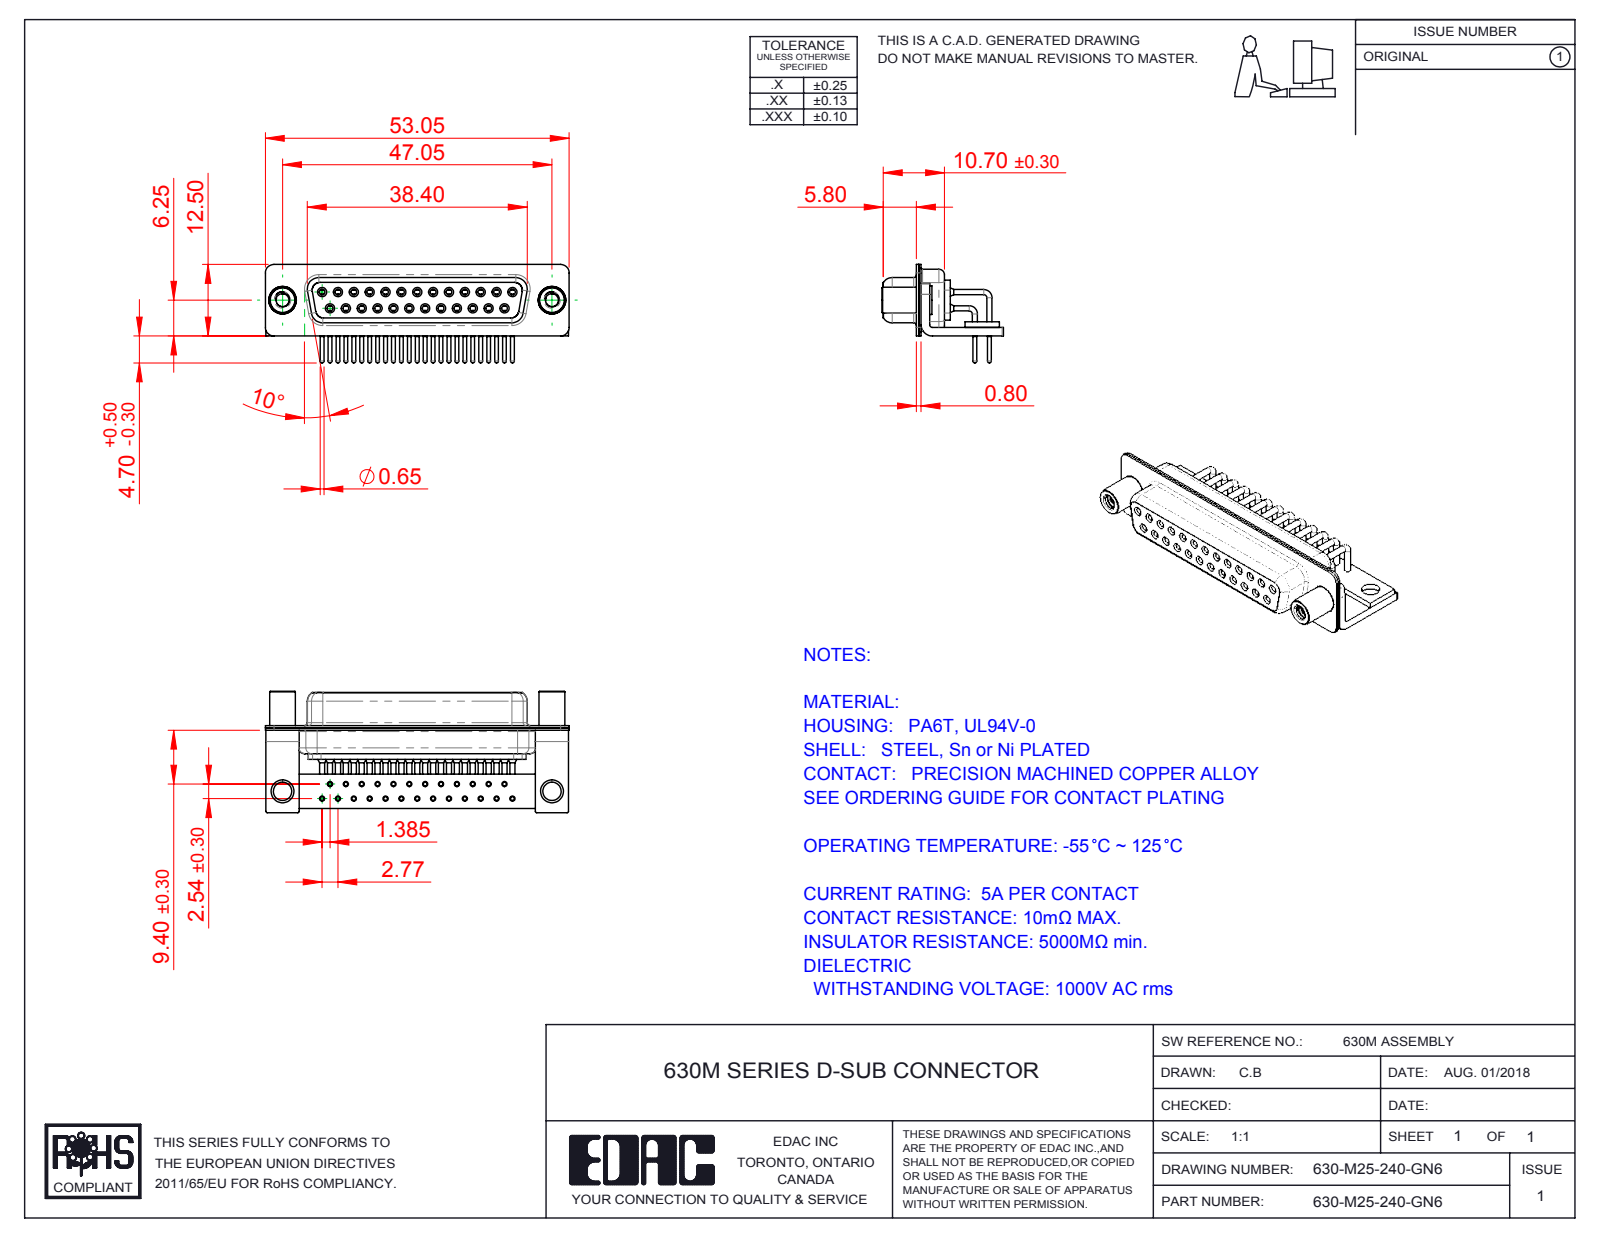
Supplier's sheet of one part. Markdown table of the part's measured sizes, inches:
| quantity | value |
| --- | --- |
| part name | 630M Contact Row 1; 630-M25-240-GN6; 630M Shell Front_25 Contacts; 630M Contact Row 2 (+5 more) |
| STEP written by | SolidWorks 2016 (CONFIG_CONTROL_DESIGN) |
| units | inches |
| bodies | 33 solids, 1754 faces (470 planar, 826 cylindrical, 458 other) |
| overall size | 2.089 × 0.835 × 0.677 |
| volume | 0.279 in³ |
| surface area | 17.7 in² |
| round holes (diameter × count) | 0.035 × 25, 0.039 × 25, 0.043 × 25, 0.067 × 25, 0.071 × 25, 0.079 × 25, 0.089 × 2, 0.126 × 2, 0.157 × 2, 0.189 × 2 |
| round bosses / shafts (diameter × count) | 0.063 × 25, 0.059 × 25, 0.035 × 25, 0.026 × 25, 0.197 × 2, 0.193 × 2, 0.177 × 2 |
| partial cylindrical surfaces (radius × count) | 0.01 × 16, 0.059 × 16, 0.079 × 13, 0.053 × 10, 0.063 × 8, 0.02 × 5, 0.024 × 4, 0.026 × 4 |
| main face-to-face distances | 0.016, 0.091, 0.075, 0.057, 0.352, 0.033, 0.368, 0.031, 0.244, 0.039 |
| hole center spacings | 0.109, 0.218, 0.327, 0.436, 0.545, 0.124, 0.192, 0.654 |
